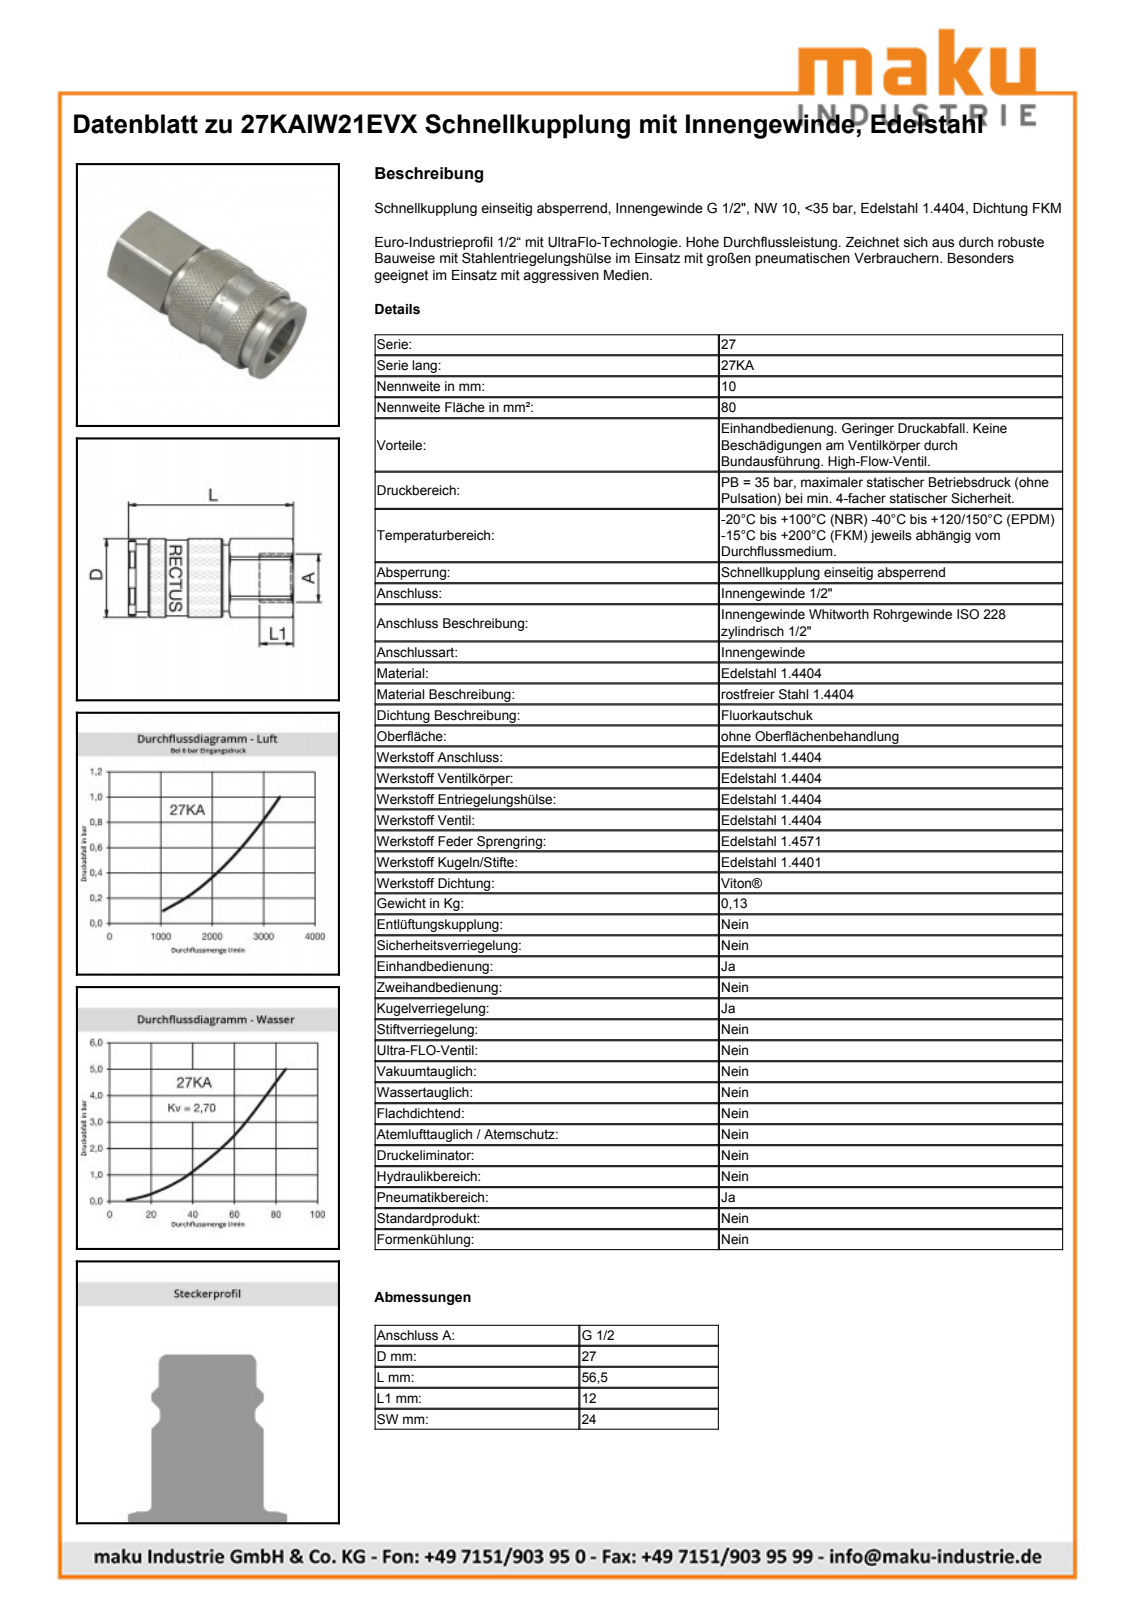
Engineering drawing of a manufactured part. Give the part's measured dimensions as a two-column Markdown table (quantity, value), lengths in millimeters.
| quantity | value |
| --- | --- |
| part name | D104963 |
| STEP written by | Autodesk Inventor 2011 (AUTOMOTIVE_DESIGN) |
| units | millimeters |
| bodies | 1 solid, 734 faces (322 planar, 80 cylindrical, 332 other) |
| overall size | 56.45 × 27.15 × 27.15 |
| volume | 24 112 mm³ |
| surface area | 10 088 mm² |
| round holes (diameter × count) | 20.96 × 1, 23.35 × 1, 23.55 × 1 |
| round bosses / shafts (diameter × count) | 27.15 × 1, 26 × 1, 23.1 × 1, 22.75 × 1, 22.55 × 1, 21.75 × 1 |
| partial cylindrical surfaces (radius × count) | 12.9 × 1, 13.53 × 1 |
| main face-to-face distances | 24, 44.45, 23.98, 12.7, 31.75, 6.25, 25.5, 38.2, 2.5, 3.75 |
